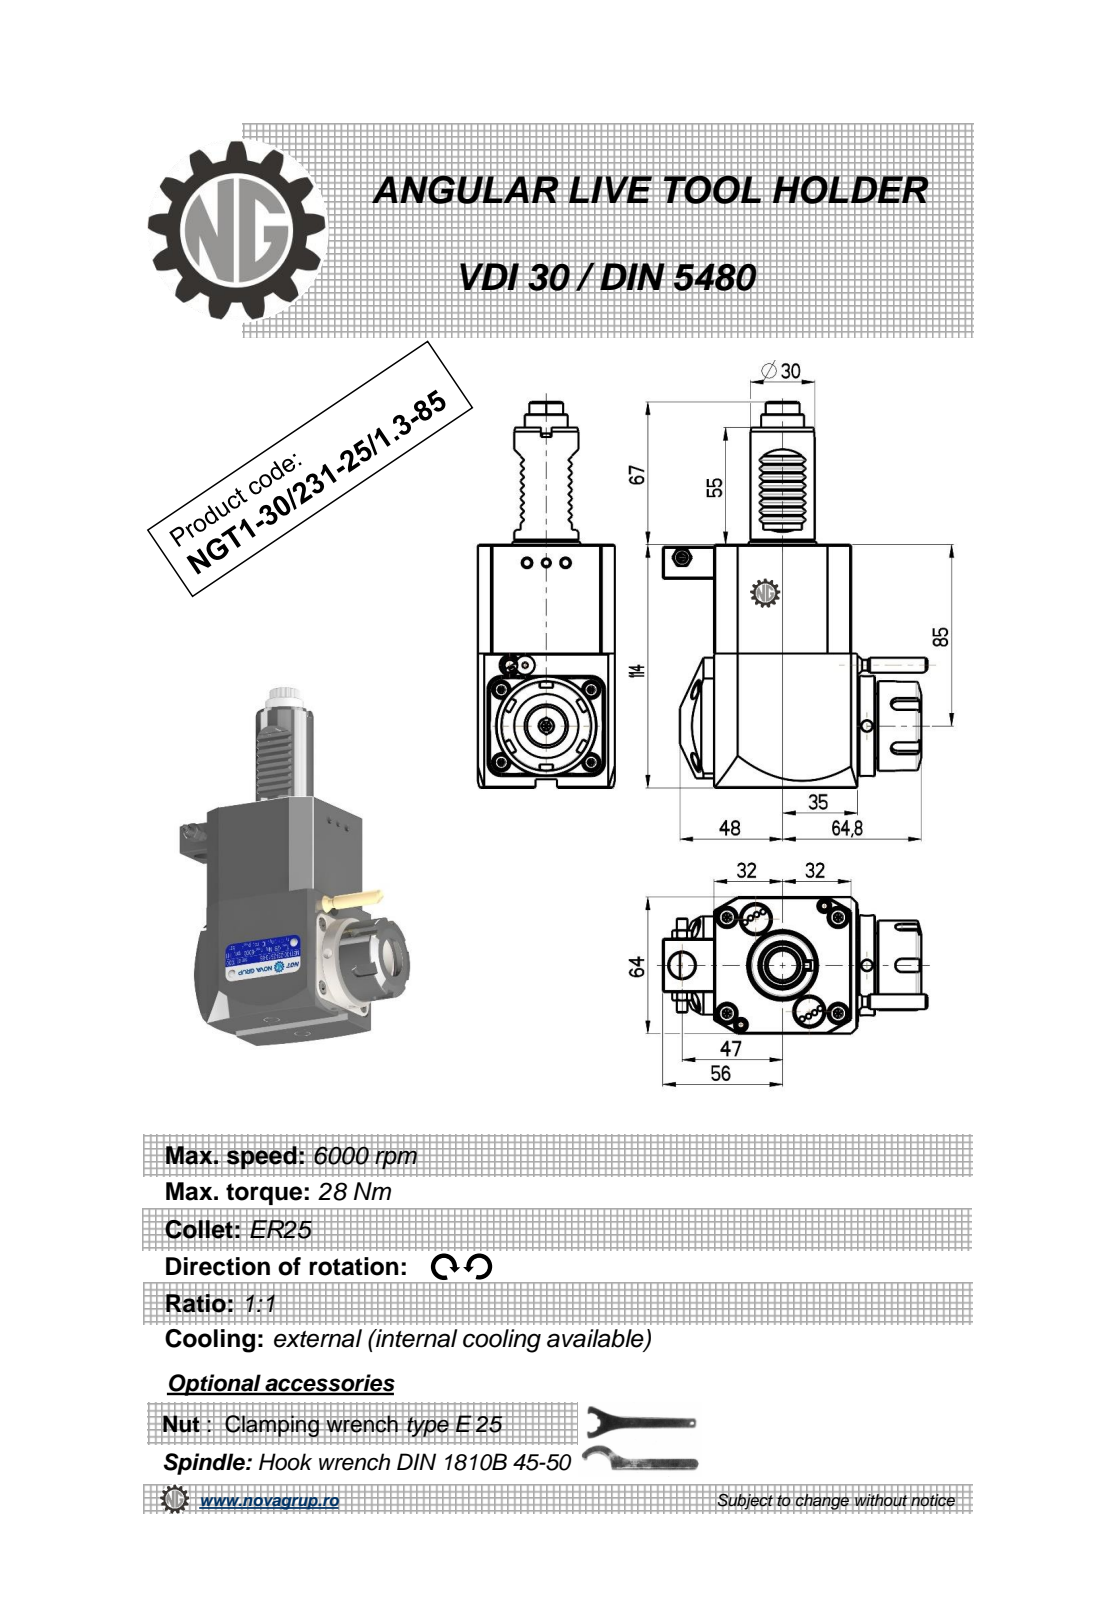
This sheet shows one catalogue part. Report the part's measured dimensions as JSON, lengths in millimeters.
{"part_name": "NGT1_30_231_25_1_3_85", "step_written_by": "PRO/ENGINEER BY PARAMETRIC TECHNOLOGY CORPORATION, 2010280 (CONFIG_CONTROL_DESIGN)", "units": "millimeters", "bodies": {"solids": 1, "faces": 562, "planar": 227, "cylindrical": 165, "other": 170}, "overall_size": [181, 123.83, 64], "volume_mm3": 575398, "surface_area_mm2": 55302, "round_holes": [[5, 2], [2.5, 1], [3, 1], [4.2, 1], [9.5, 1], [12, 1], [20.3, 1]], "round_bosses_or_shafts": [[8.96, 2], [5, 2], [47, 1], [42, 1], [35, 1], [30, 1], [20, 1], [7, 1]], "partial_cylinders_radius": [[1.98, 36], [0.3, 16], [0.26, 12], [3, 5], [3.5, 4], [160, 2], [7.08, 1], [7.92, 1]], "face_to_face_distances": [64, 114, 0.5, 67, 67.2, 3.2, 76.42, 7.5, 8, 3], "hole_center_spacings": [33.19, 50.92, 76.5, 86.45, 117.11]}
